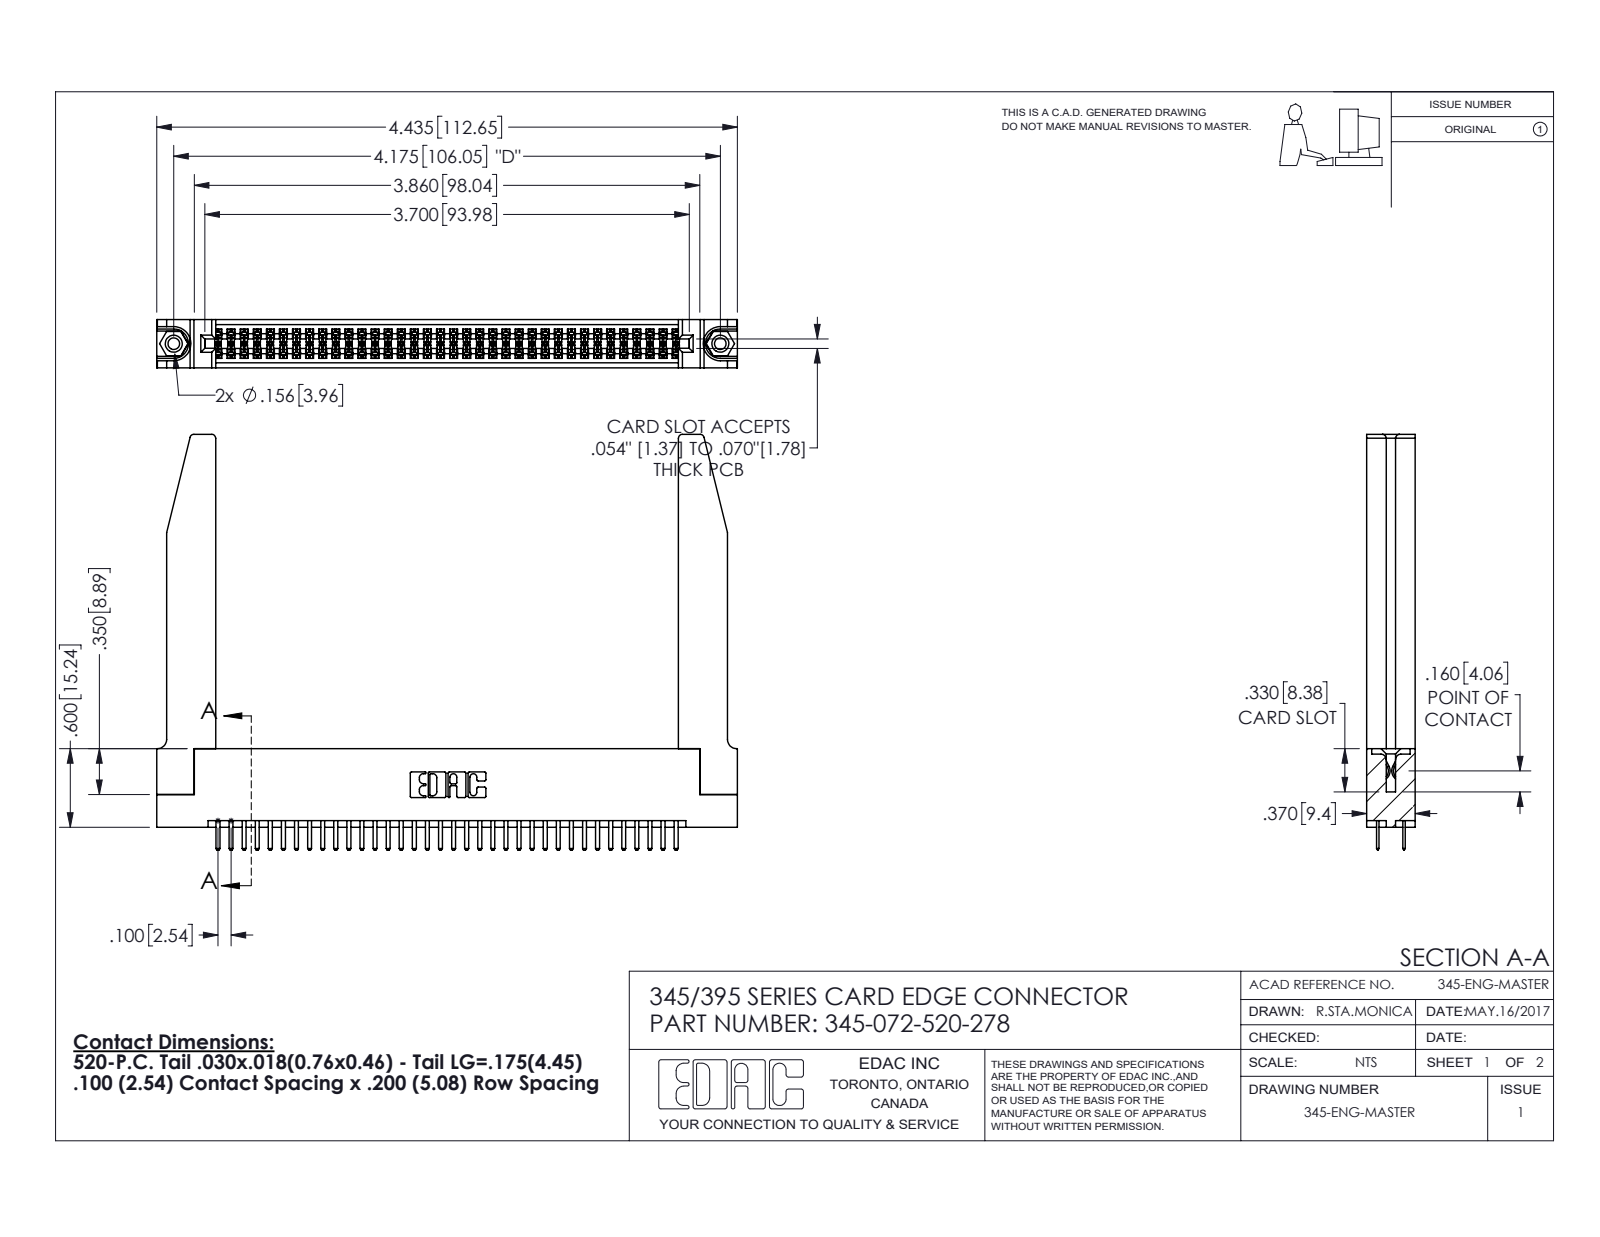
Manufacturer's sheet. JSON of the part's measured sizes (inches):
{"part_name": "345-292-001_345-293-120; 345 Part_Flush Mounting Lugs - 0.156 Dia-TH; 345-220-078_345-220-078; 345-072-520-278 (+1 more)", "step_written_by": "SolidWorks 2016 (CONFIG_CONTROL_DESIGN)", "units": "inches", "bodies": {"solids": 77, "faces": 4248, "planar": 2742, "cylindrical": 1454, "other": 52}, "overall_size": [4.436, 3.175, 0.37], "volume_in3": 1.137, "surface_area_in2": 35.19, "round_holes": [[0.089, 2], [0.125, 2], [0.156, 2], [0.064, 1]], "round_bosses_or_shafts": [[0.155, 2]], "partial_cylinders_radius": [[0.006, 108], [0.01, 76], [0.01, 22], [0.03, 8], [0.007, 6], [0.031, 6], [0.026, 3], [0.014, 2]], "face_to_face_distances": [0.37, 0.072, 0.298, 0.2, 0.098, 0.272, 0.025, 0.225, 0.022, 0.175], "hole_center_spacings": [0.27, 3.939, 4.175]}
